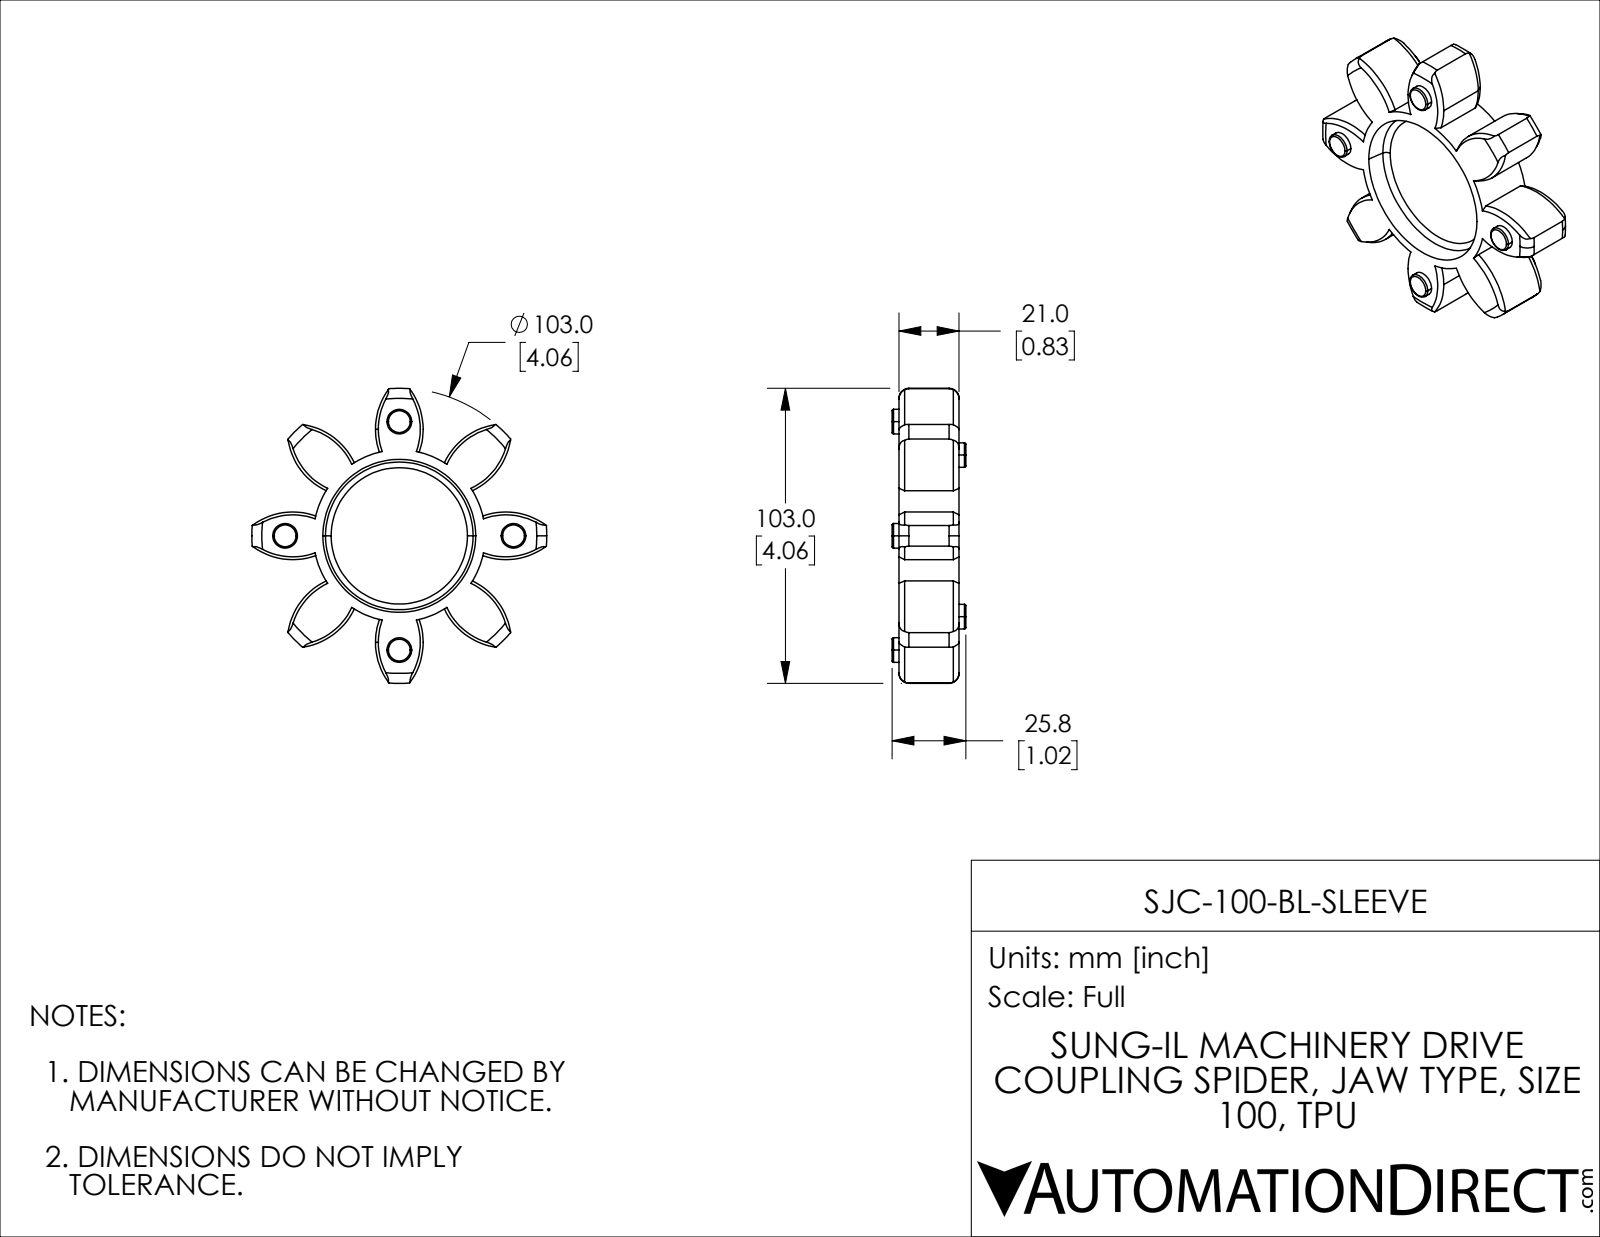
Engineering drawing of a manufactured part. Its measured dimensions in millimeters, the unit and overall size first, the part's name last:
Units: millimetres
Overall size (bounding box): 103 × 103 × 25.8
Round bosses / shafts (diameter × count): ⌀8.6 ×8
Partial cylindrical surfaces — rounded edges, fillets, slot ends (radius × count): R23.73 ×8, R30 ×1, R51.5 ×1
Main face-to-face distances: 7.7, 13.3, 21, 5.6, 2.4, 10.1, 15.7, 23.4, 25.8
Volume: 79 152 mm³ · Surface area: 23 000 mm²
Bodies: 1 solid, 141 faces (12 planar, 51 cylindrical, 78 other)
Part name (STEP PRODUCT): SJC-100-BL-SLEEVE
STEP written by: SolidWorks 2021 (CONFIG_CONTROL_DESIGN)
